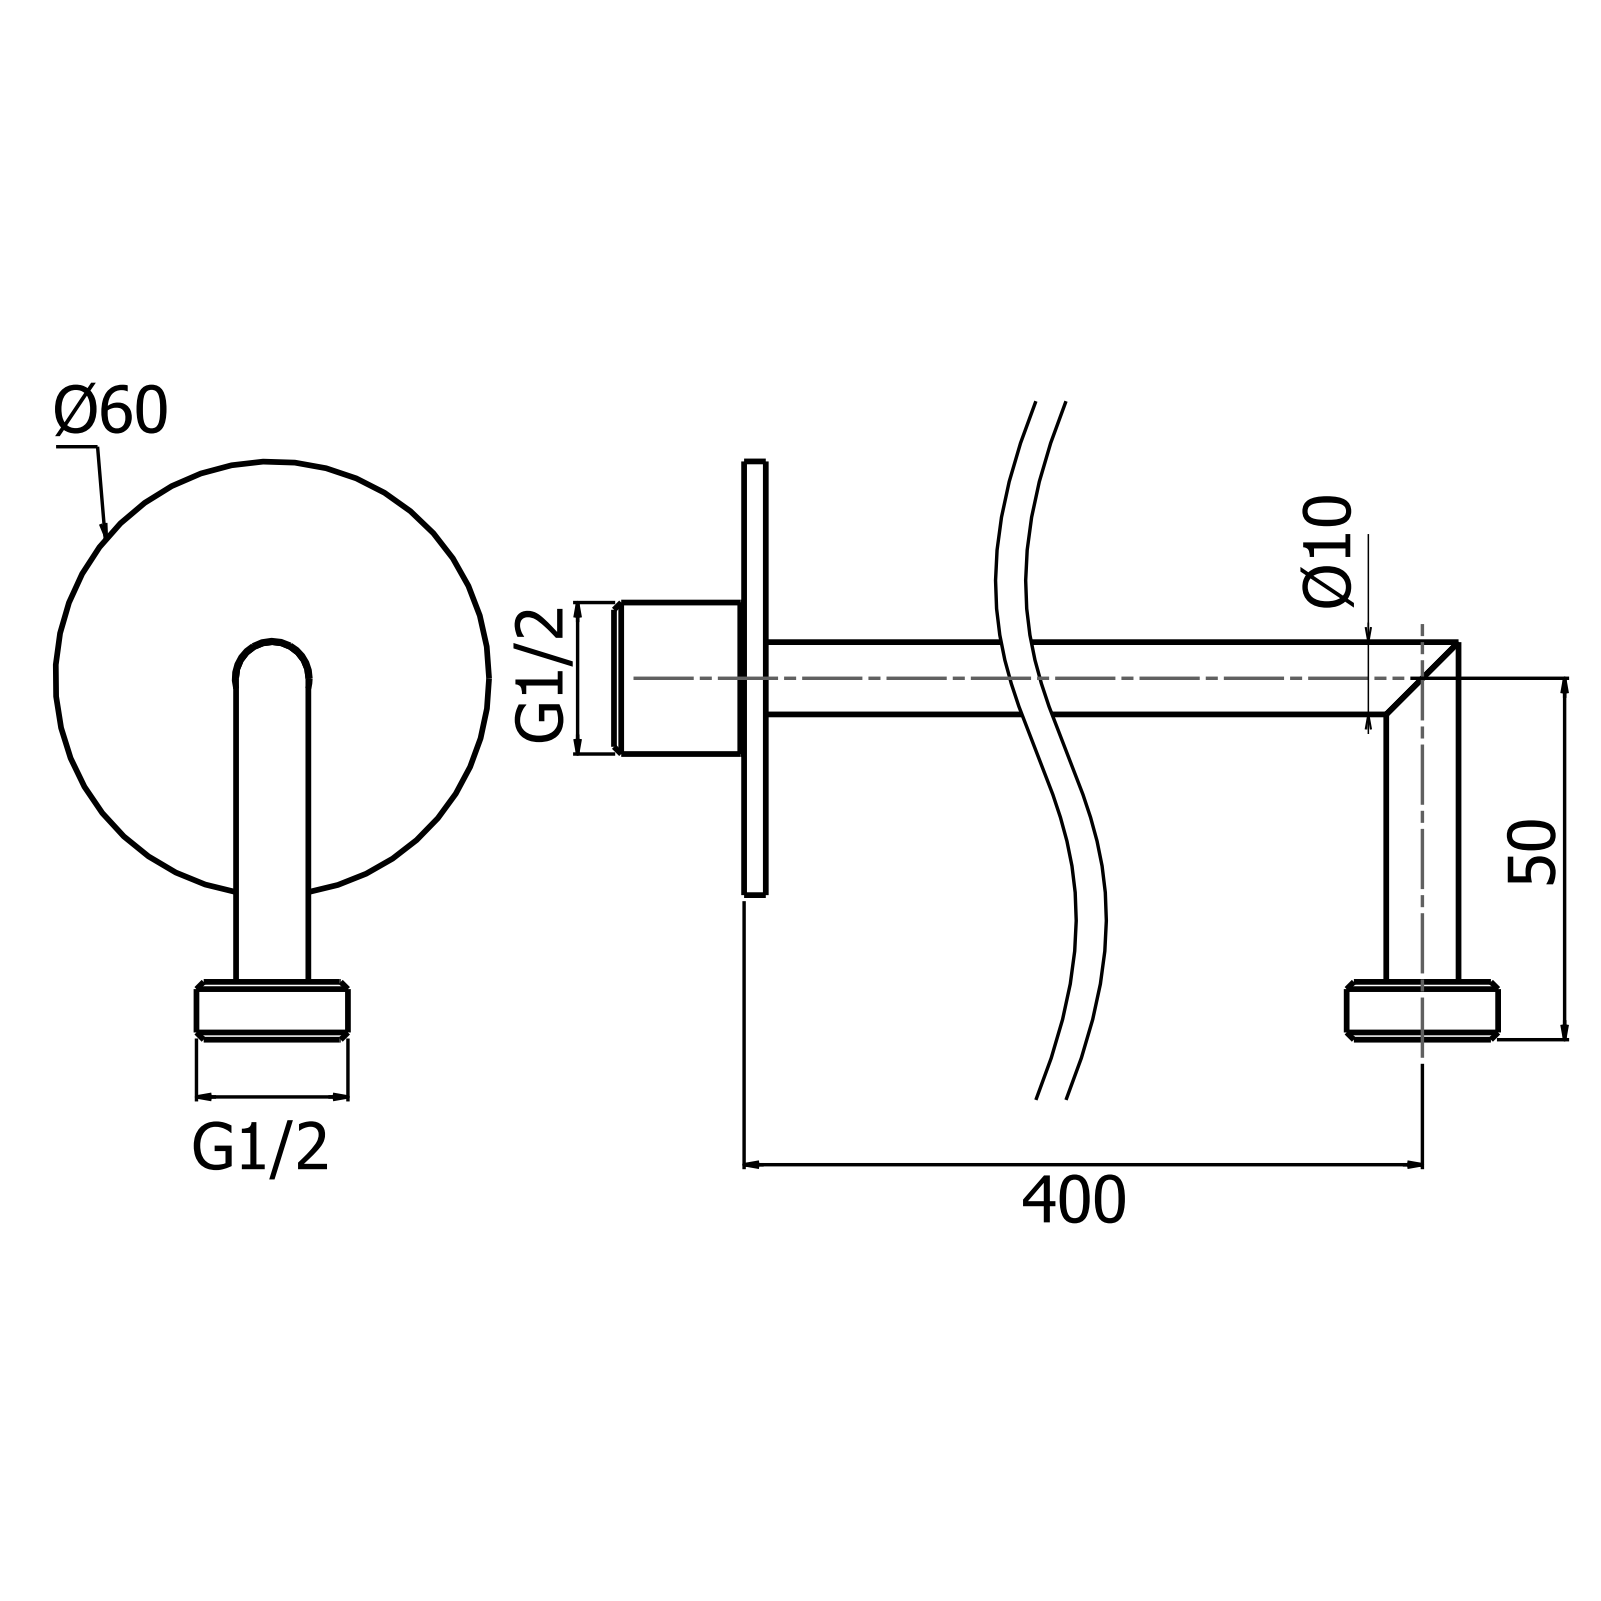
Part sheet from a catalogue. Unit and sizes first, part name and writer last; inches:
Units: inches
Overall size (bounding box): 16.831 × 3.15 × 2.362
Round holes (diameter × count): ⌀0.276 ×2, ⌀0.409 ×1, ⌀0.551 ×1, ⌀0.646 ×1
Round bosses / shafts (diameter × count): ⌀0.394 ×2, ⌀2.362 ×1, ⌀0.825 ×1
Partial cylindrical surfaces — rounded edges, fillets, slot ends (radius × count): R0.413 ×1
Main face-to-face distances: 0.118, 0.315, 0.622, 0.504, 0.827, 0.709, 0.205, 16.004, 16.122, 16.626
Volume: 2.002 in³ · Surface area: 50.68 in²
Bodies: 1 solid, 26 faces (10 planar, 11 cylindrical, 5 other)
Part name (STEP PRODUCT): A.R._24540/20220905
STEP written by: Spatial InterOp 3D (AUTOMOTIVE_DESIGN)
